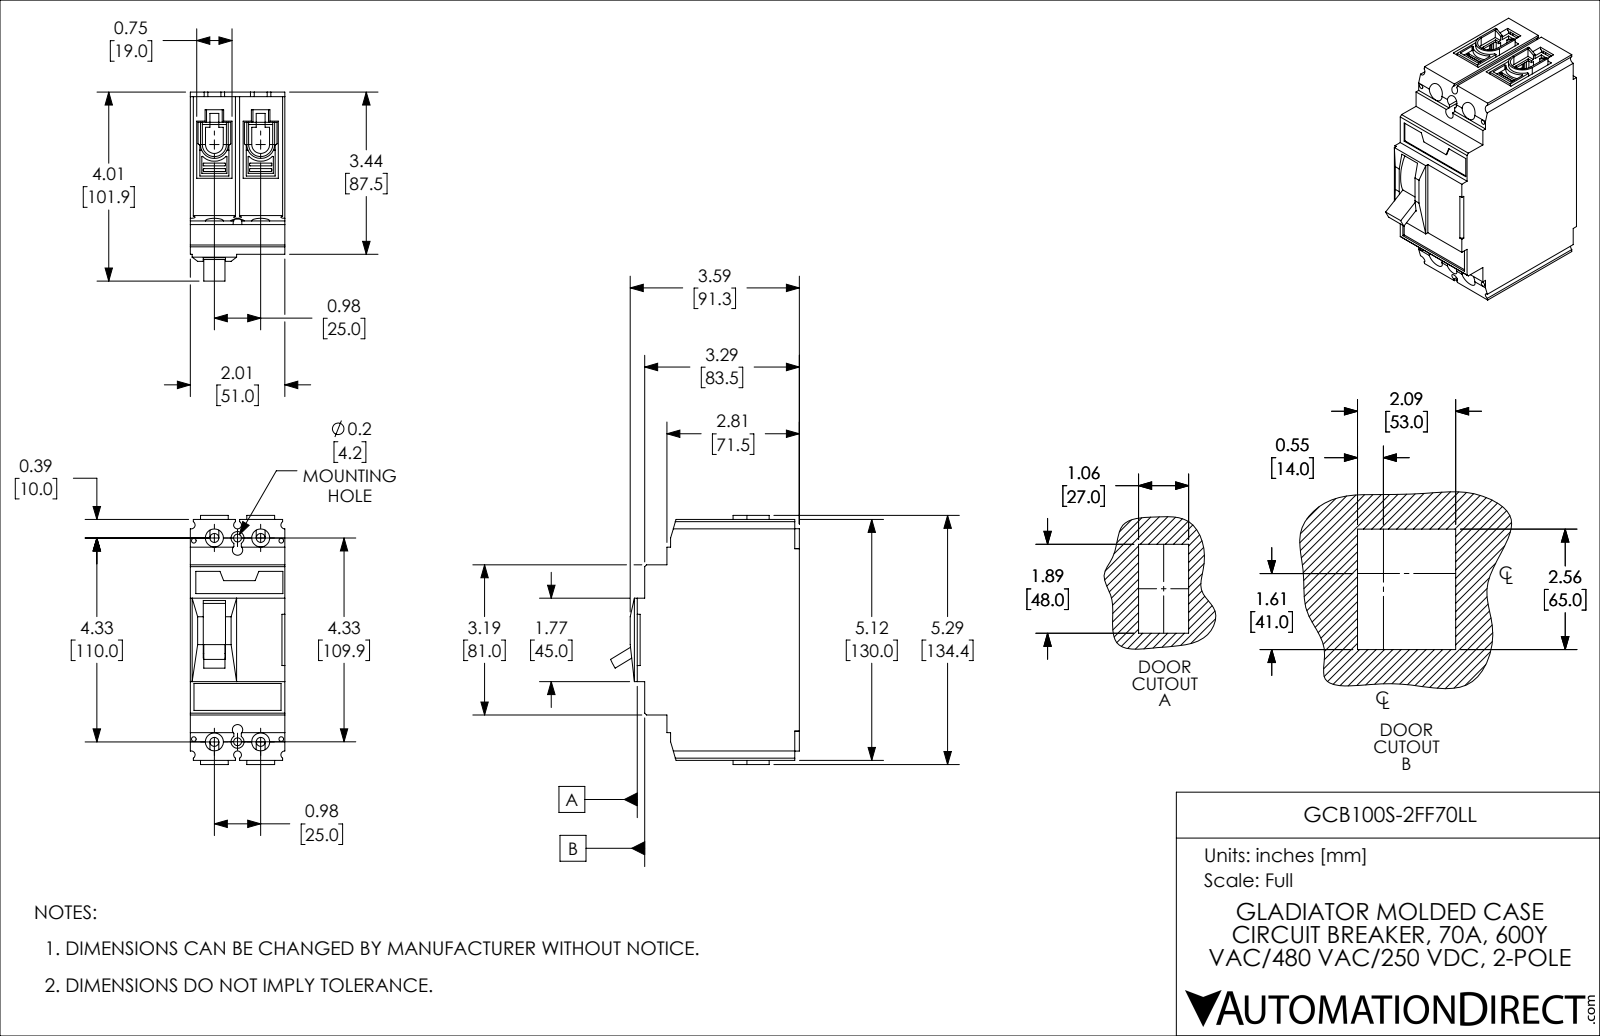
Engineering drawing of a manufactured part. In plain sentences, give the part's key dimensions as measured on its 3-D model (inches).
The part is named "GCB100S-2FF70LL". Its 3-D file was written by "SolidWorks 2021 (CONFIG_CONTROL_DESIGN)". It is 1 solid with 839 faces: 529 planar, 278 cylindrical and 32 other. Overall it measures 5.291 by 4.013 by 2.008 inches. Its volume is 29.1 cubic inches and its surface area 110.4 square inches. Round holes: 4 of diameter 0.098, 4 of diameter 0.165, 4 of diameter 0.189, 4 of diameter 0.382, 2 of diameter 0.276. Partial cylindrical surfaces (rounded edges, fillets, slot ends): 58 of radius 0.012, 26 of radius 0.02, 10 of radius 0.039, 10 of radius 0.157, 4 of radius 0.024, 4 of radius 0.083, 2 of radius 0.11, 2 of radius 0.189. The main face-to-face distances are 2.008, 0.984, 0.622, 4.496, 0.748, 1.87, 0.11, 0.886, 1.122, 0.138. The hole center spacings are 0.441, 0.492, 0.564, 0.931, 0.987, 1.422, 4.294, 4.357.
